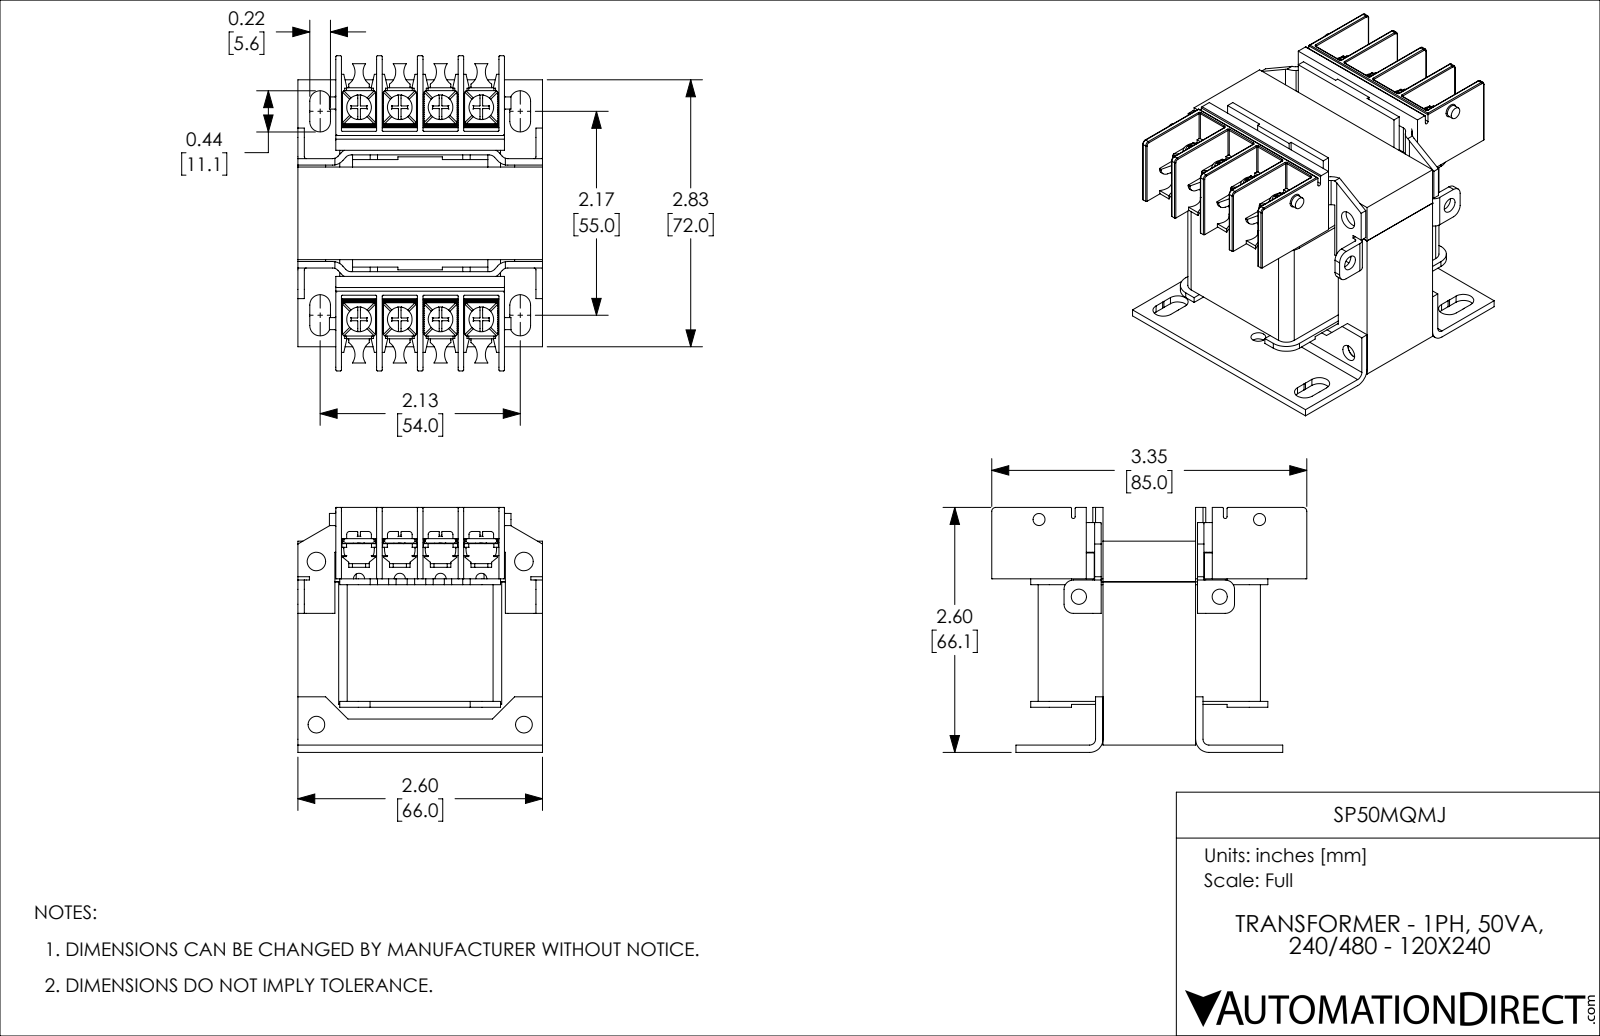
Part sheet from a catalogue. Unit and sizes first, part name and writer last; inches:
Units: inches
Overall size (bounding box): 3.346 × 2.601 × 2.598
Round holes (diameter × count): ⌀0.157 ×10, ⌀0.105 ×8, ⌀0.138 ×8, ⌀0.161 ×2, ⌀0.177 ×2, ⌀0.197 ×2
Round bosses / shafts (diameter × count): ⌀0.262 ×8, ⌀0.24 ×8, ⌀0.168 ×8, ⌀0.11 ×8, ⌀0.128 ×3
Partial cylindrical surfaces — rounded edges, fillets, slot ends (radius × count): R0.005 ×52, R0.01 ×52, R0.012 ×46, R0.029 ×32, R0.157 ×16, R0.039 ×14, R0.035 ×12, R0.079 ×10
Main face-to-face distances: 0.433, 1.732, 0.866, 0.404, 0.463, 0.03, 1.299, 0.059, 1.329, 0.984
Hole centre spacings: 0.433, 0.866, 2.283, 1.299, 2.242, 2.404, 2.274, 2.293
Volume: 9.38 in³ · Surface area: 117.4 in²
Bodies: 41 solids, 3078 faces (1860 planar, 926 cylindrical, 292 other)
Part name (STEP PRODUCT): SP50MQMJ
STEP written by: SolidWorks 2018 (AUTOMOTIVE_DESIGN)
